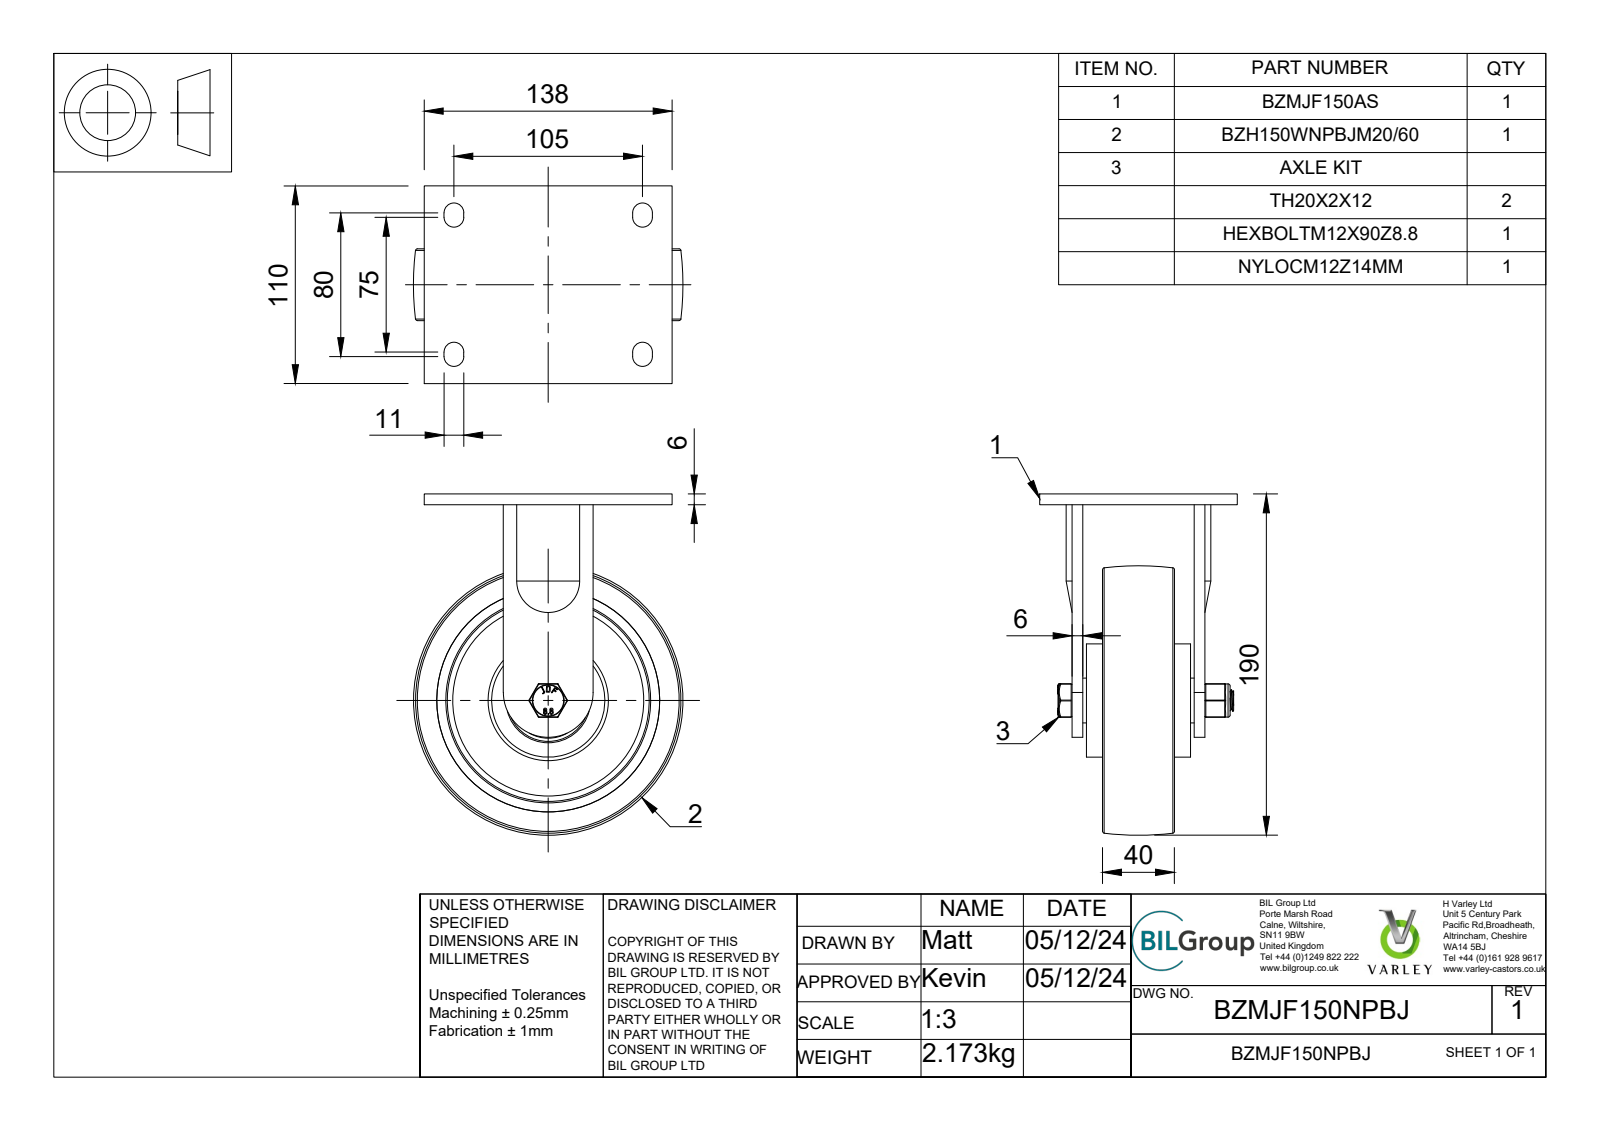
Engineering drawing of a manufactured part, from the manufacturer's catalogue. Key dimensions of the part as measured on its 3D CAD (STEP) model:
Part name (STEP PRODUCT): BZMJF150NPBJ v3; BZMJF150AS - 62 v1; STEEL FABRICATED BRACKET; BZH150WNPBJM2060 v1 (+7 more)
STEP written by: Autodesk Translation Framework v13.20.0.188 (AP242_MANAGED_MODEL_BASED_3D_ENGINEERING_MIM_LF)
Units: millimetres
Bodies: 35 solids, 998 faces (396 planar, 190 cylindrical, 412 other)
Overall size (bounding box): 190 × 150 × 110
Volume: 648 289 mm³ · Surface area: 220 276 mm²
Round holes (diameter × count): ⌀12 ×1, ⌀12.2 ×1, ⌀13 ×1, ⌀14 ×1, ⌀20 ×1, ⌀28.5 ×1, ⌀30.8 ×1, ⌀40.3 ×1, ⌀40.5 ×1, ⌀42 ×1, ⌀47 ×1, ⌀124 ×1
Round bosses / shafts (diameter × count): ⌀63 ×1, ⌀40.8 ×1, ⌀31.3 ×1, ⌀27 ×1, ⌀25 ×1, ⌀24 ×1, ⌀19.8 ×1, ⌀18.5 ×1
Partial cylindrical surfaces — rounded edges, fillets, slot ends (radius × count): R0.5 ×20, R5.5 ×8, R0.47 ×4, R0.9 ×4, R48.72 ×4, R0.89 ×2, R0.89 ×2, R6.78 ×2
Main face-to-face distances: 6, 16.75, 23.25, 11, 57, 27.75, 34.25, 51, 17, 33.75
